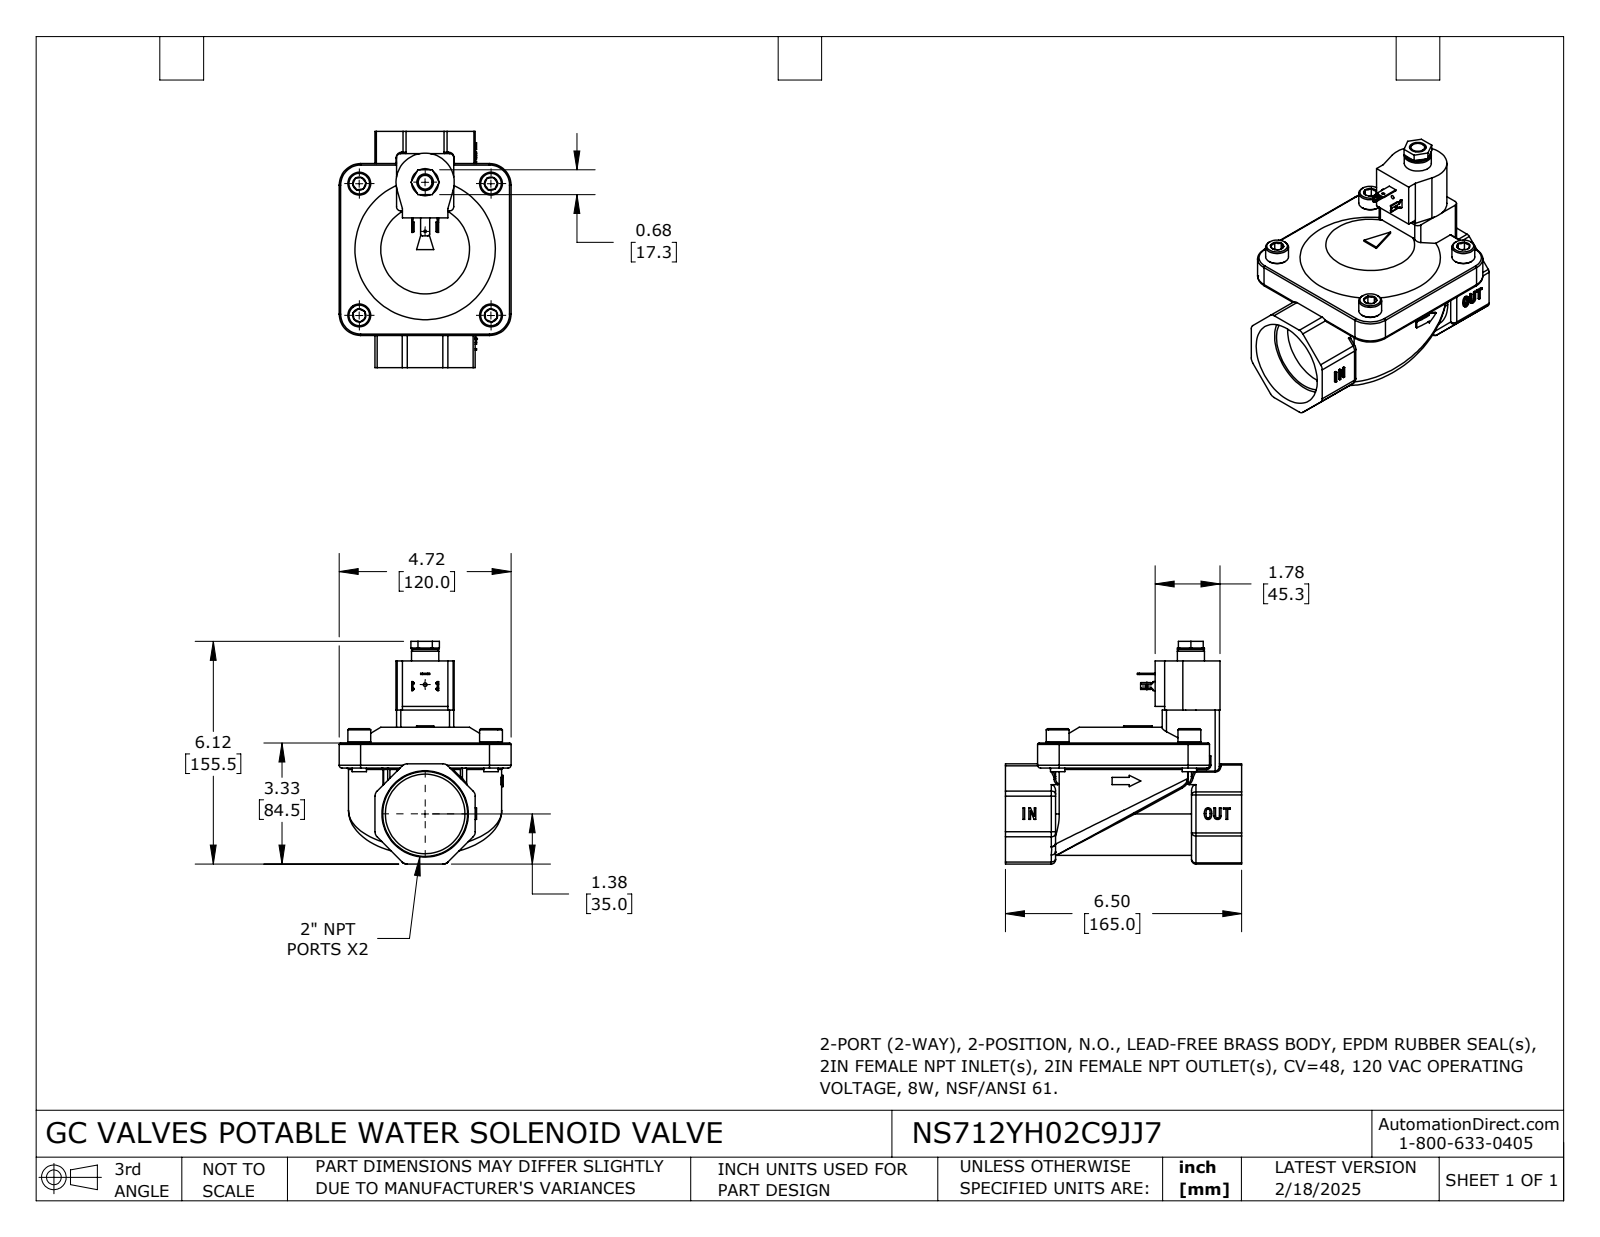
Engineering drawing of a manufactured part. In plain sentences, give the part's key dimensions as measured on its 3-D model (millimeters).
The part is named "NS712YH02C9JJ7". Its 3-D file was written by "SolidWorks 2024 (CONFIG_CONTROL_DESIGN)". It is 1 solid with 478 faces: 205 planar, 136 cylindrical and 137 other. Overall it measures 165 by 155.51 by 120 millimeters. Its volume is 914 905 cubic millimeters and its surface area 96 823 square millimeters. Round holes: 1 of diameter 1.68, 1 of diameter 1.7, 1 of diameter 2.53, 1 of diameter 11.58, 1 of diameter 55.58. Round bosses or shafts: 4 of diameter 16, 4 of diameter 10, 1 of diameter 18.95. Partial cylindrical surfaces (rounded edges, fillets, slot ends): 28 of radius 3, 21 of radius 1, 10 of radius 5, 4 of radius 0.15, 4 of radius 1.04, 4 of radius 2, 4 of radius 15, 2 of radius 1.27. The main face-to-face distances are 17.5, 69.99, 95, 11, 40, 28.5, 25, 70, 120, 142.5. The hole center spacings are 34.29, 90.26.
